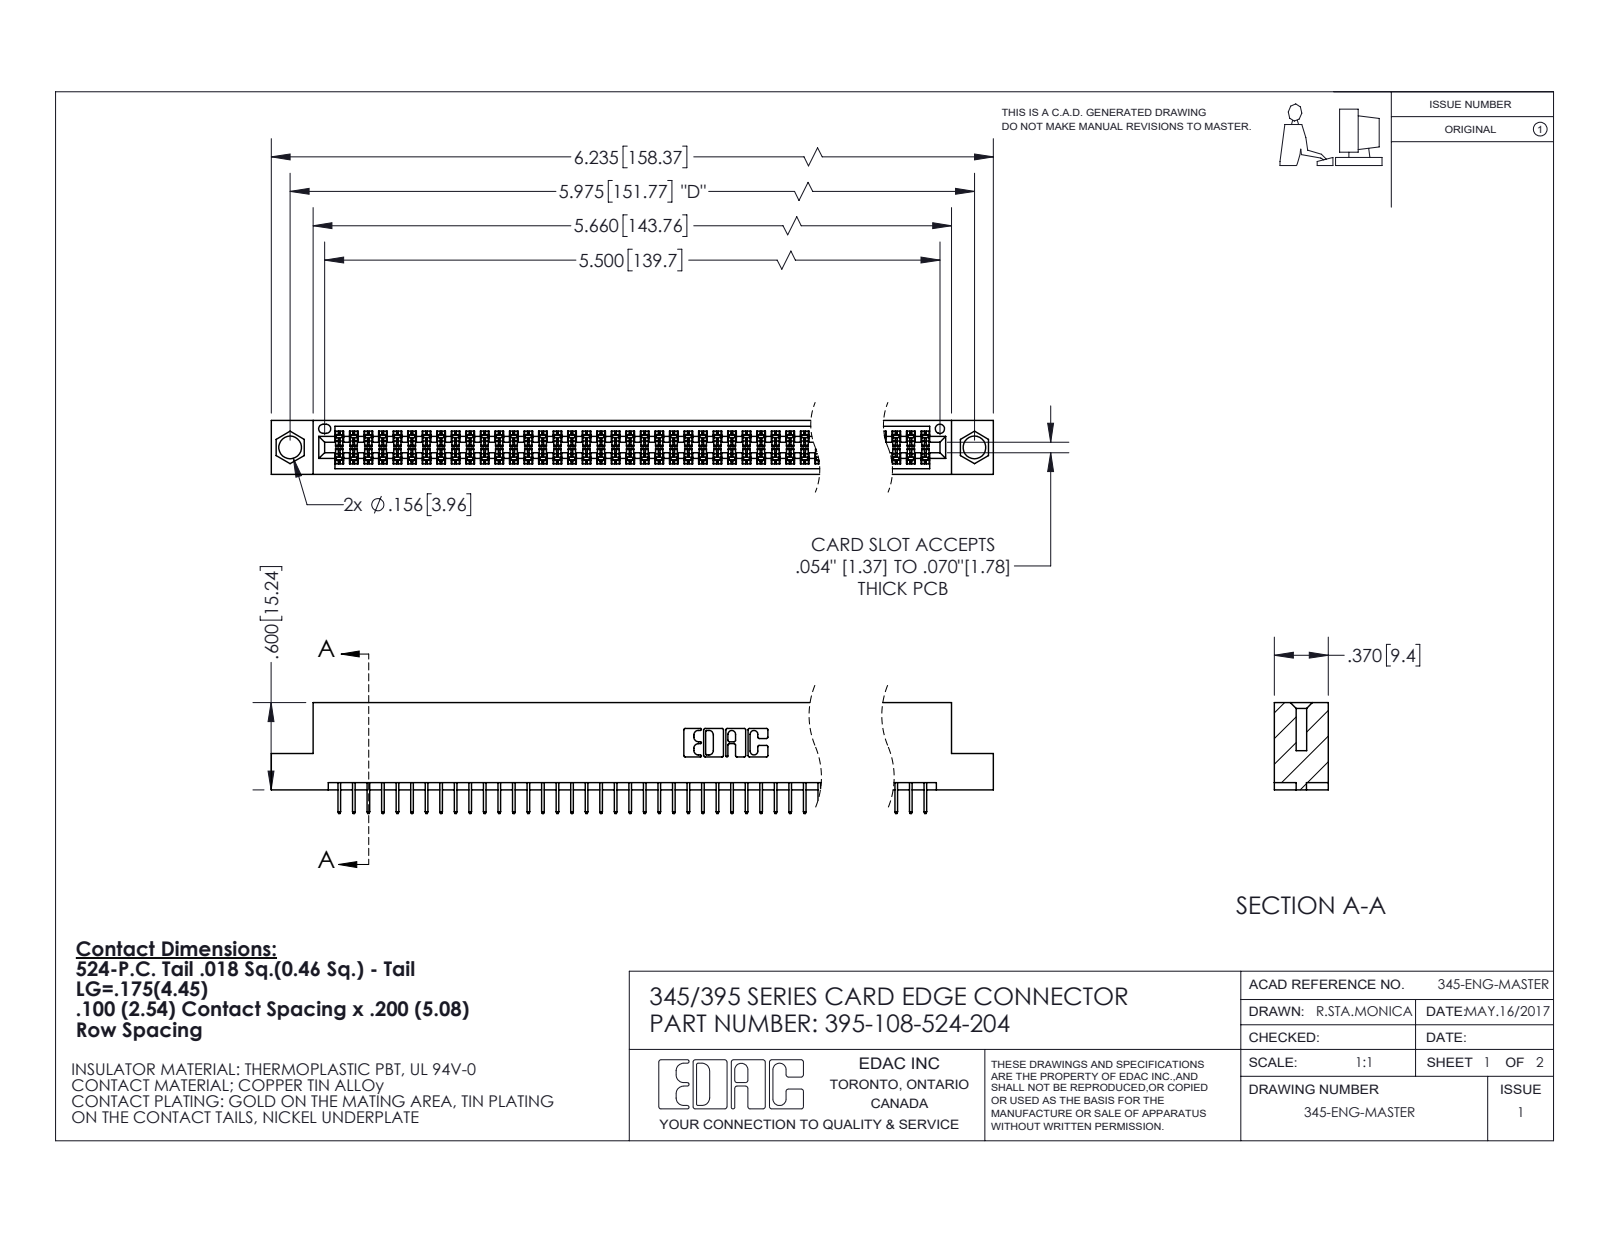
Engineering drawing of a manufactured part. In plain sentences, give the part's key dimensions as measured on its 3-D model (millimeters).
The part is named "345 Part_Flush Mounting Lugs - 0.156 Dia-TI; 395-108-524-204; 345-292-001_345-293-124". Its 3-D file was written by "SolidWorks 2020 (CONFIG_CONTROL_DESIGN)". It is 109 solids with 5972 faces: 4306 planar, 1666 cylindrical and 0 other. Overall it measures 158.4 by 19.4 by 9.4 millimeters. Its volume is 15 200 cubic millimeters and its surface area 22 160 square millimeters. Round holes: 2 of diameter 4, 1 of diameter 1.6. Partial cylindrical surfaces (rounded edges, fillets, slot ends): 163 of radius 0.2, 22 of radius 0.3, 6 of radius 0.2, 6 of radius 0.8, 3 of radius 0.7, 2 of radius 0.4, 2 of radius 0.5, 2 of radius 0.6. The main face-to-face distances are 1.8, 7.6, 5.1, 9.4, 2.5, 6.9, 0.6, 5.7, 1.8, 4.4. The hole center spacings are 6.9, 145.8, 151.8.
